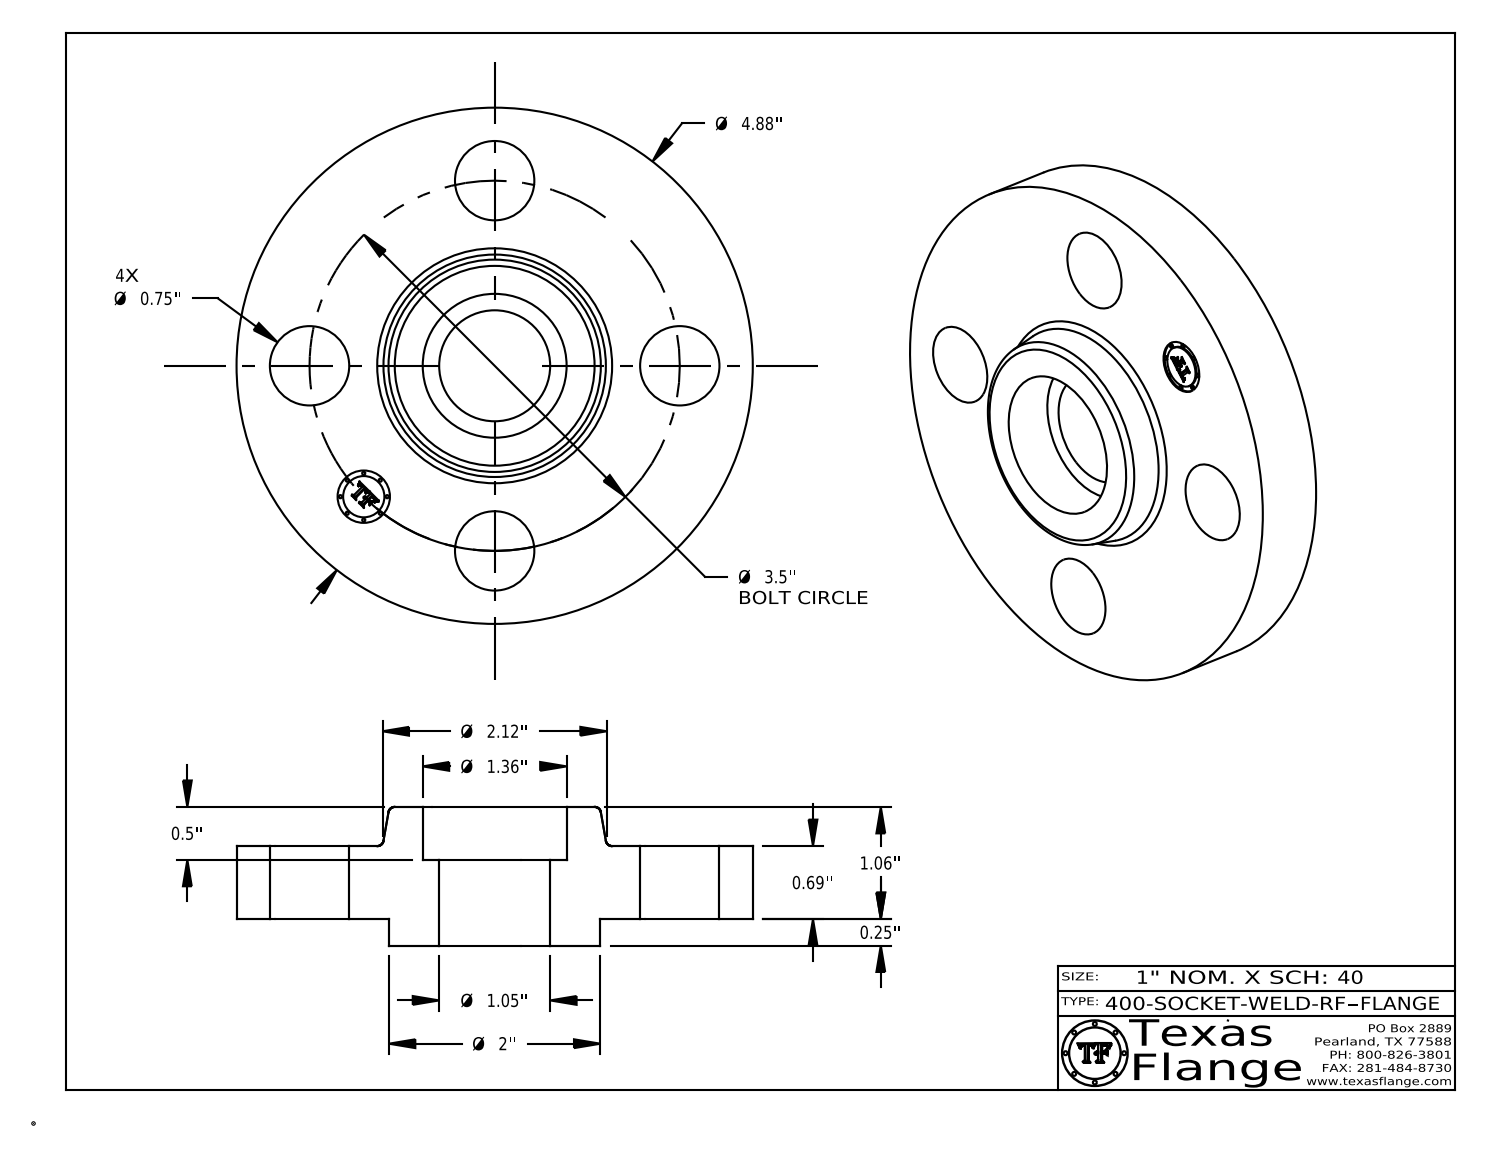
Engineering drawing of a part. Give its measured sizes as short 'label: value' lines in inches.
name: 400-SOCKET-WELD-RF
written by: CATIA V5 STEP AP214 (AUTOMOTIVE_DESIGN)
unit: in
bodies: 1 solid, 412 faces (370 planar, 36 cylindrical, 6 other)
size: 4.88 × 4.88 × 1.31
volume: 12.27 in³; area: 57.48 in²
holes: 4× ⌀0.75, 1× ⌀0.495, 1× ⌀1.049, 1× ⌀1.36
bosses: 8× ⌀0.03, 1× ⌀4.88, 1× ⌀2, 1× ⌀0.39
face distances: 0.69, 0.25, 0.94, 1.31, 1.06, 0.37, 0.81, 0.56, 0.13, 0.5
hole spacings: 1.75, 2.475, 1.339, 3.233, 3.5
